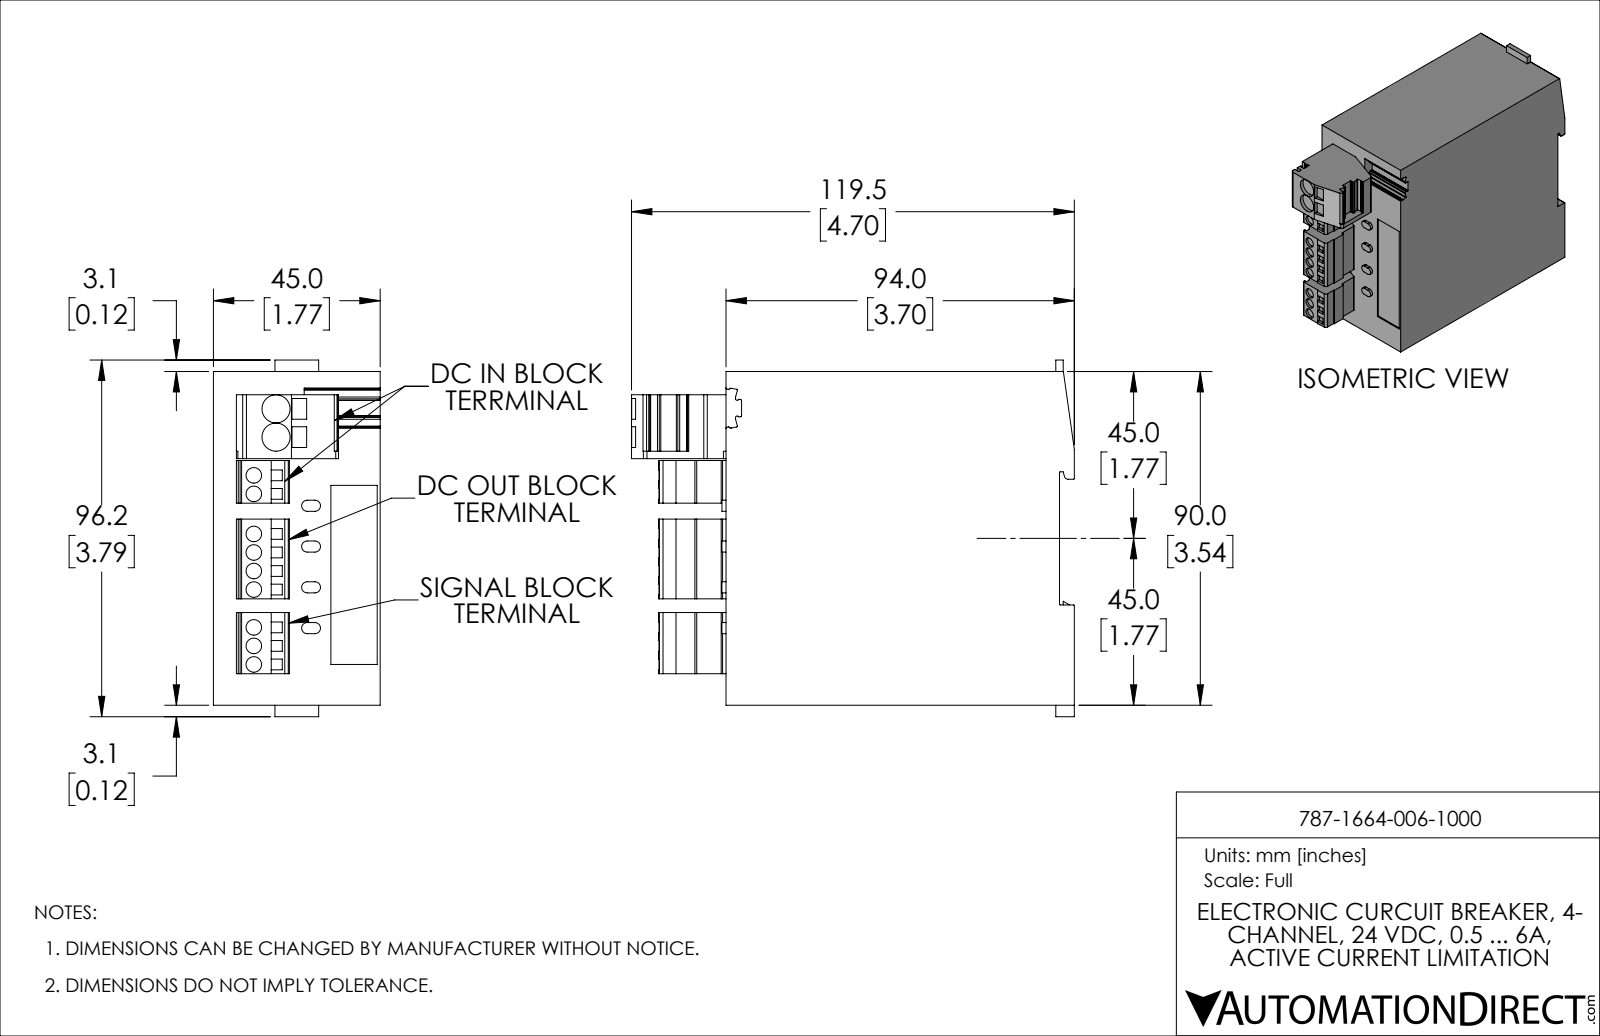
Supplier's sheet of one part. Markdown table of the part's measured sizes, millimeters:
| quantity | value |
| --- | --- |
| part name | 787-1664/006-1000 |
| STEP written by | PARTsolutions (CONFIG_CONTROL_DESIGN) |
| units | millimeters |
| bodies | 1 solid, 328 faces (248 planar, 80 cylindrical, 0 other) |
| overall size | 119.5 × 96.2 × 45 |
| volume | 393 125 mm³ |
| surface area | 41 275 mm² |
| round holes (diameter × count) | 4.2 × 9, 7.6 × 2 |
| partial cylindrical surfaces (radius × count) | 0.2 × 25, 1.5 × 8, 1 × 7, 0.4 × 6, 0.3 × 4, 0.49 × 4, 2 × 1 |
| main face-to-face distances | 45, 90, 4, 94, 0.5, 38.8, 6.2, 23.5, 66.5, 16.5 |
| hole center spacings | 5, 10, 20.2, 25.2, 15.2, 15.8, 20.8, 25.8 |
